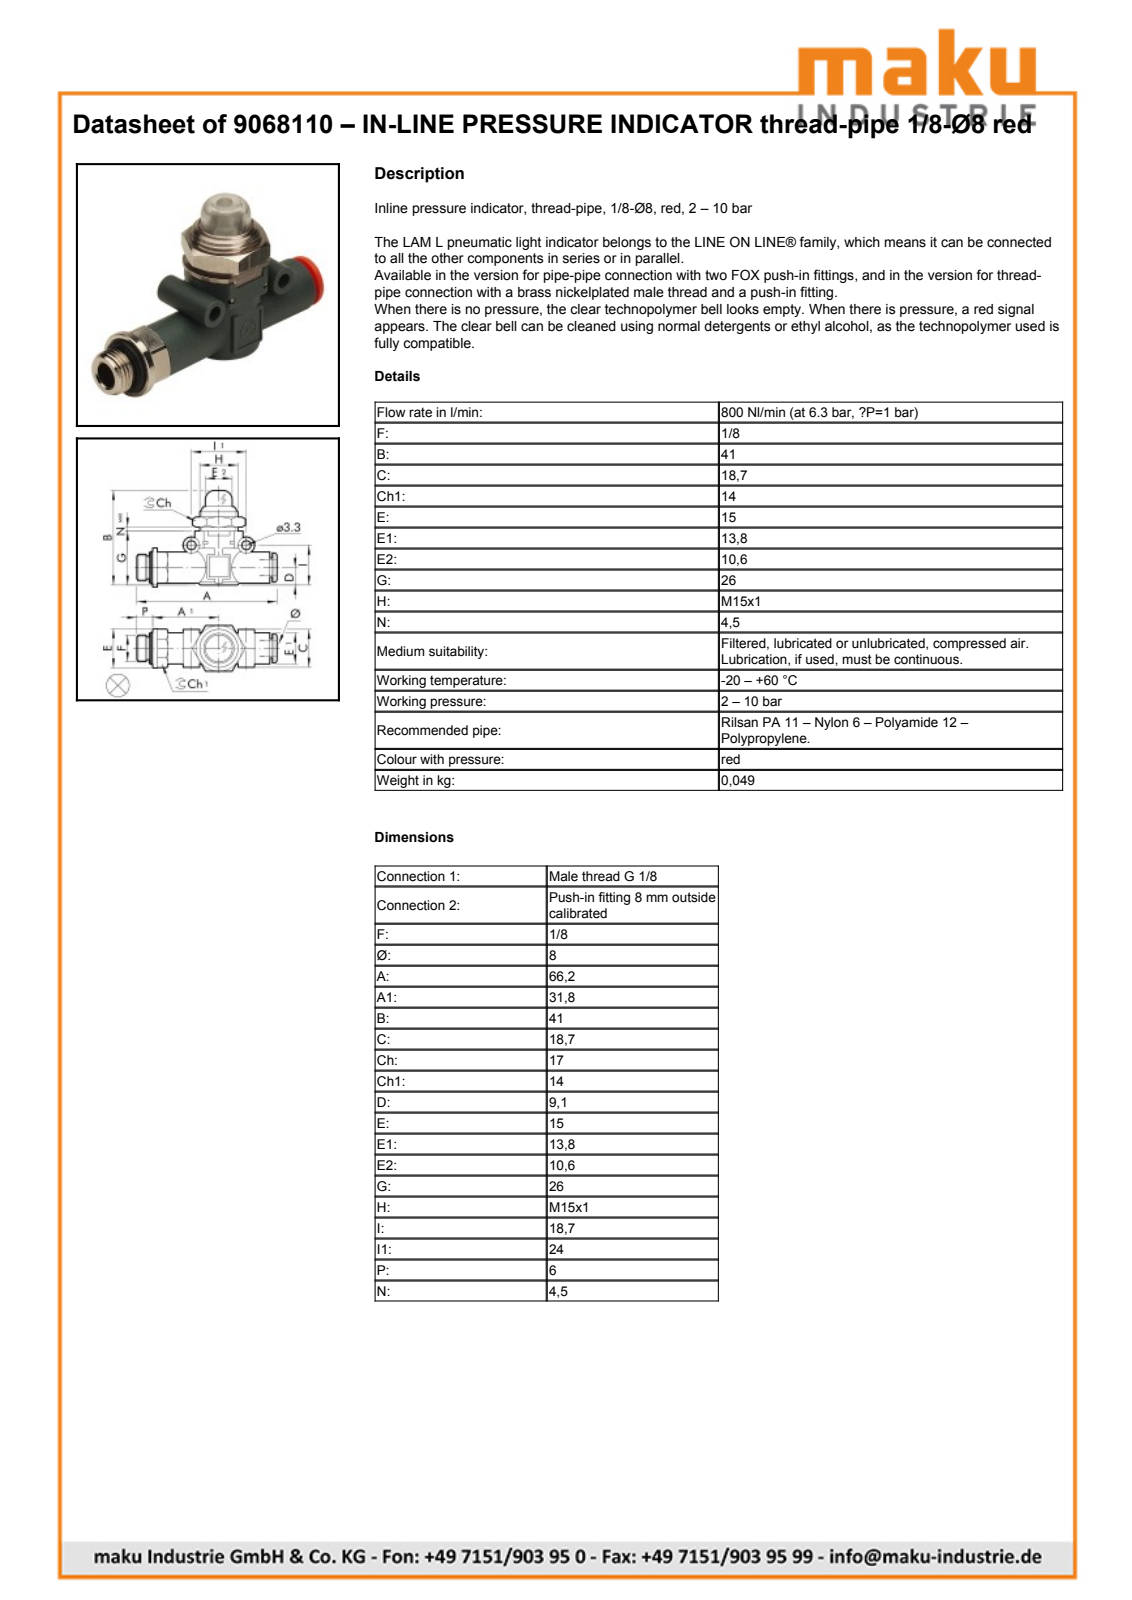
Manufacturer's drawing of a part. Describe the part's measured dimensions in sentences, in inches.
The part is named "9068110; LINE-ON-LINE D8 V2v/V3V_L body; LINE-ON-LINE D8 VNR-L bushing; LINE-ON-LINE D8-1/8 thread port (+1 more)". Its 3-D file was written by "PARTsolutions (AUTOMOTIVE_DESIGN)". It is 4 solids with 189 faces: 105 planar, 58 cylindrical and 26 other. Overall it measures 2.606 by 1.614 by 0.736 inches. Its volume is 0.655 cubic inches and its surface area 15.64 square inches. Round holes: 2 of diameter 0.13, 2 of diameter 0.236, 1 of diameter 0.197, 1 of diameter 0.217, 1 of diameter 0.319, 1 of diameter 0.433, 1 of diameter 0.459, 1 of diameter 0.492, 1 of diameter 0.591. Round bosses or shafts: 2 of diameter 0.236, 1 of diameter 0.74, 1 of diameter 0.591, 1 of diameter 0.551, 1 of diameter 0.543, 1 of diameter 0.535, 1 of diameter 0.417, 1 of diameter 0.383. Partial cylindrical surfaces (rounded edges, fillets, slot ends): 1 of radius 0.148, 1 of radius 0.305, 1 of radius 0.38, 1 of radius 0.402, 1 of radius 0.407, 1 of radius 0.451. The main face-to-face distances are 0.949, 0.075, 0.161, 0.787, 1.024, 0.862, 0.728, 0.807, 0.02, 0.689. The hole center spacings are 0.605, 0.945.
